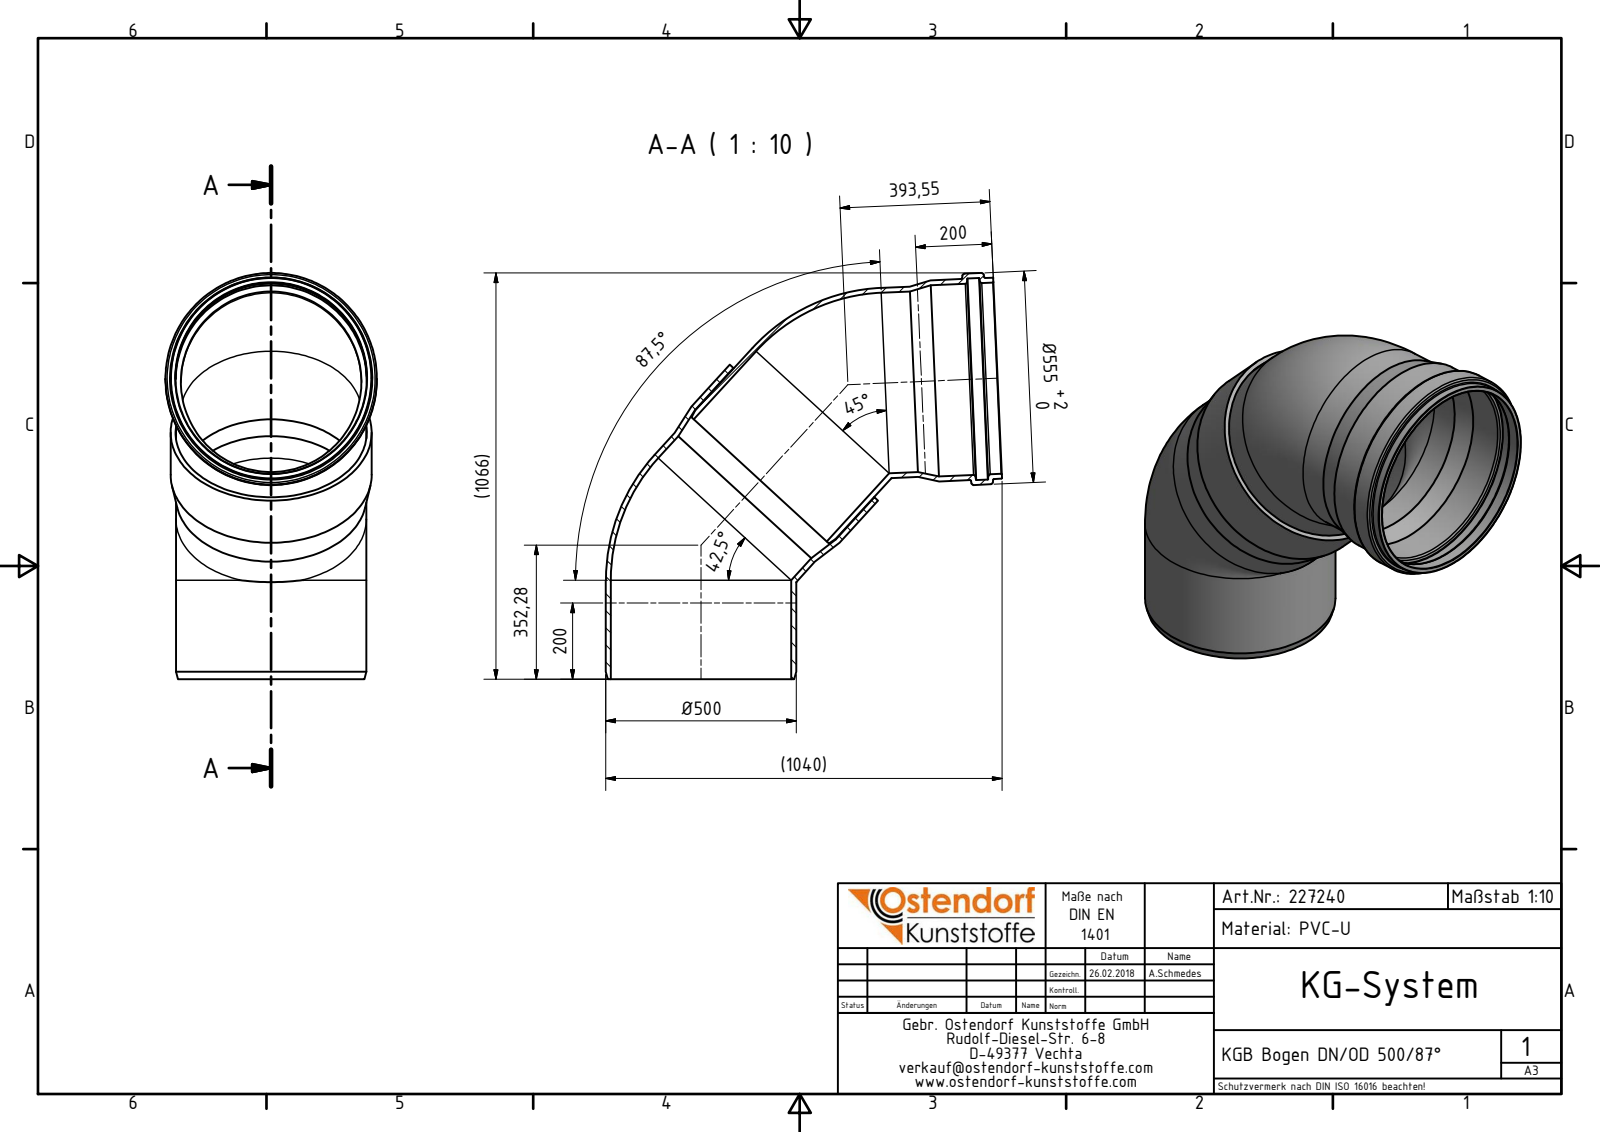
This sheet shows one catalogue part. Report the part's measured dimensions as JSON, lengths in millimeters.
{"part_name": "227240 KGB Bogen DN_OD 500_87° Teil 1; 227240 KGB Bogen DN_OD 500_87° Teil 2; 227240 KGB Bogen DN_OD 500_87°", "step_written_by": "Autodesk Inventor 2016 (AUTOMOTIVE_DESIGN)", "units": "millimeters", "bodies": {"solids": 2, "faces": 46, "planar": 4, "cylindrical": 16, "other": 26}, "overall_size": [1460.11, 728.34, 555], "volume_mm3": 28100000, "surface_area_mm2": 4708000, "round_holes": [[474, 3], [502, 3], [529, 1]], "round_bosses_or_shafts": [[528, 3], [500, 3], [555, 1]], "face_to_face_distances": [170]}
